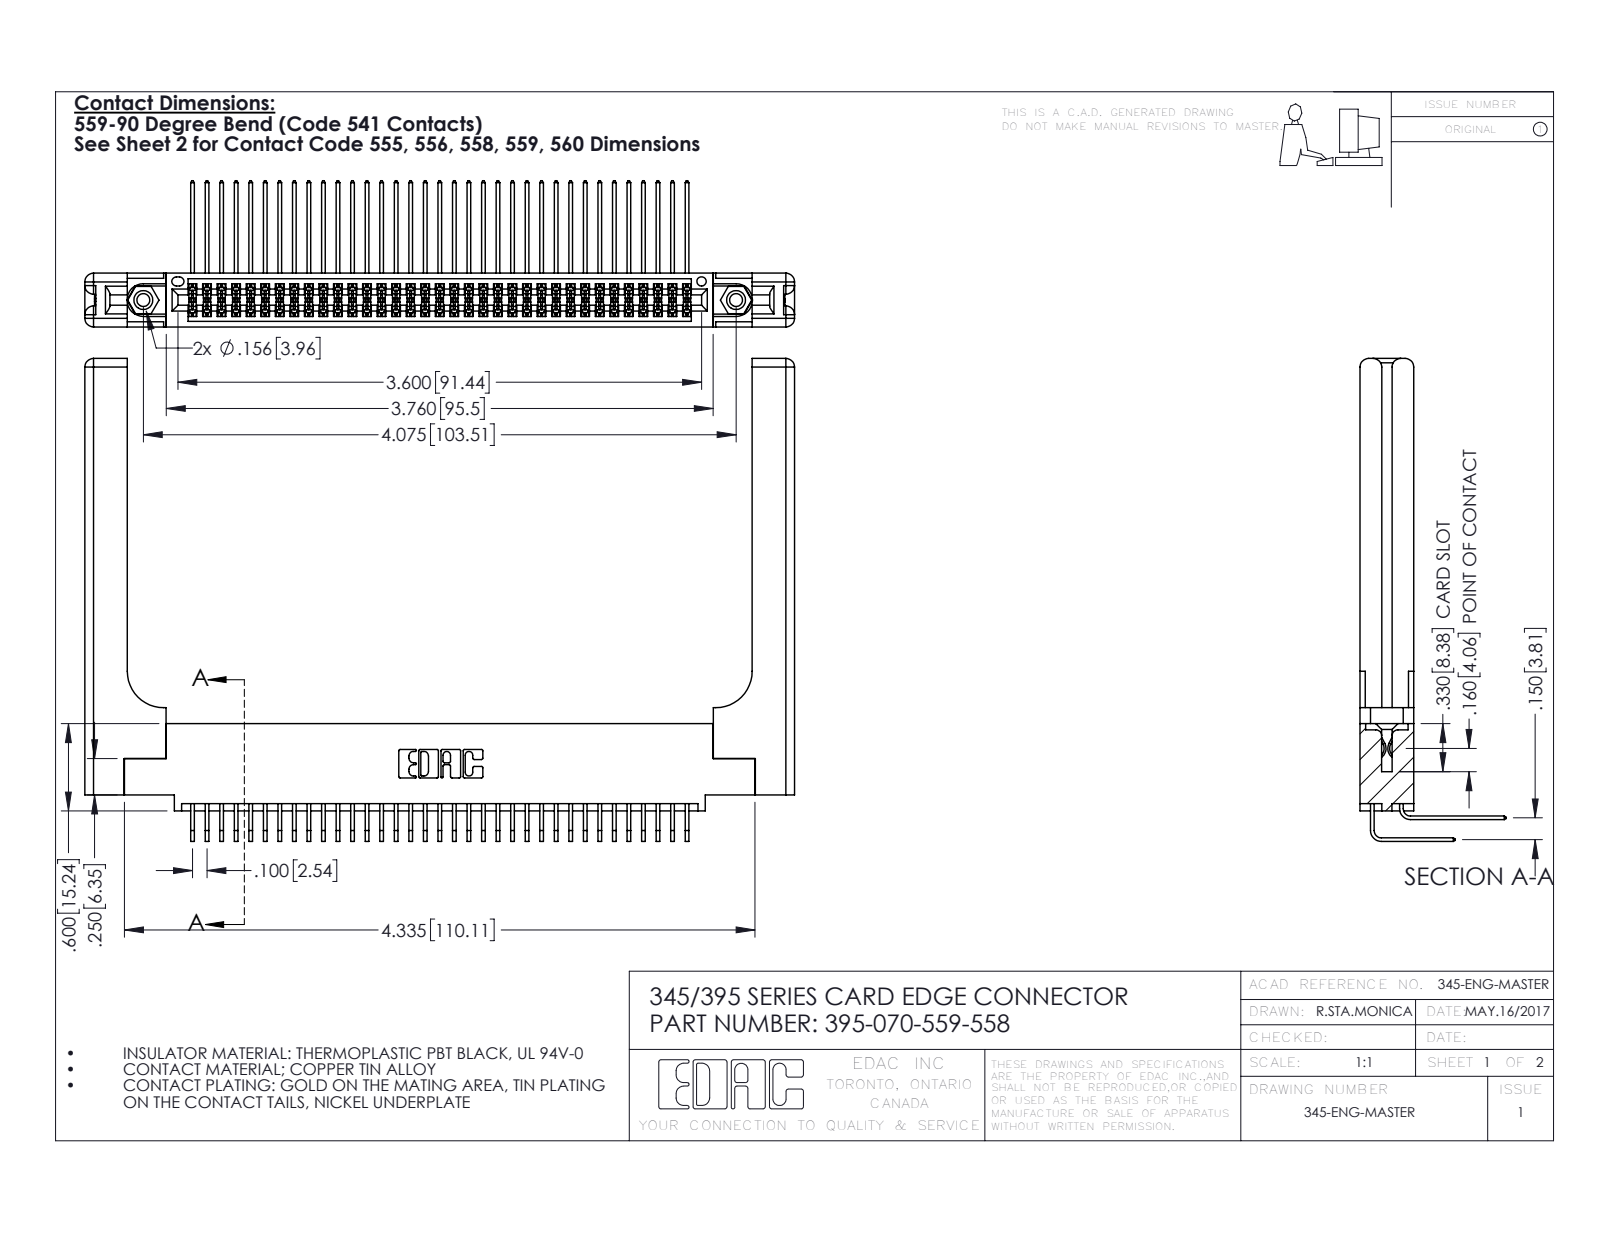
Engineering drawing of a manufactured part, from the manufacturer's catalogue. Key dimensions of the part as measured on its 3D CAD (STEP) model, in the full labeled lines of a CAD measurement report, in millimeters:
Part name (STEP PRODUCT): 345-220-058_345-220-058; 345-292-001_559 Tail - 2; 345 Part_0.110 Offset - 0.156 Dia-TH; 345-250-001_345-250-001-102 (+2 more)
STEP written by: SolidWorks 2016 (CONFIG_CONTROL_DESIGN)
Units: millimetres
Bodies: 75 solids, 4026 faces (2682 planar, 1284 cylindrical, 60 other)
Overall size (bounding box): 123.9 × 84.3 × 25.5
Volume: 20 780 mm³ · Surface area: 25 100 mm²
Round holes (diameter × count): ⌀2.3 ×2, ⌀3.2 ×2, ⌀4 ×2, ⌀1.6 ×1
Round bosses / shafts (diameter × count): ⌀3.9 ×2
Partial cylindrical surfaces — rounded edges, fillets, slot ends (radius × count): R0.2 ×105, R0.3 ×22, R1.5 ×16, R0.2 ×6, R0.8 ×6, R0.7 ×3, R0.4 ×2, R0.5 ×2
Main face-to-face distances: 1.8, 9.4, 7.6, 2.5, 6.9, 0.6, 5.1, 5.7, 3.8, 3.8
Hole centre spacings: 6.9, 97.5, 103.5
